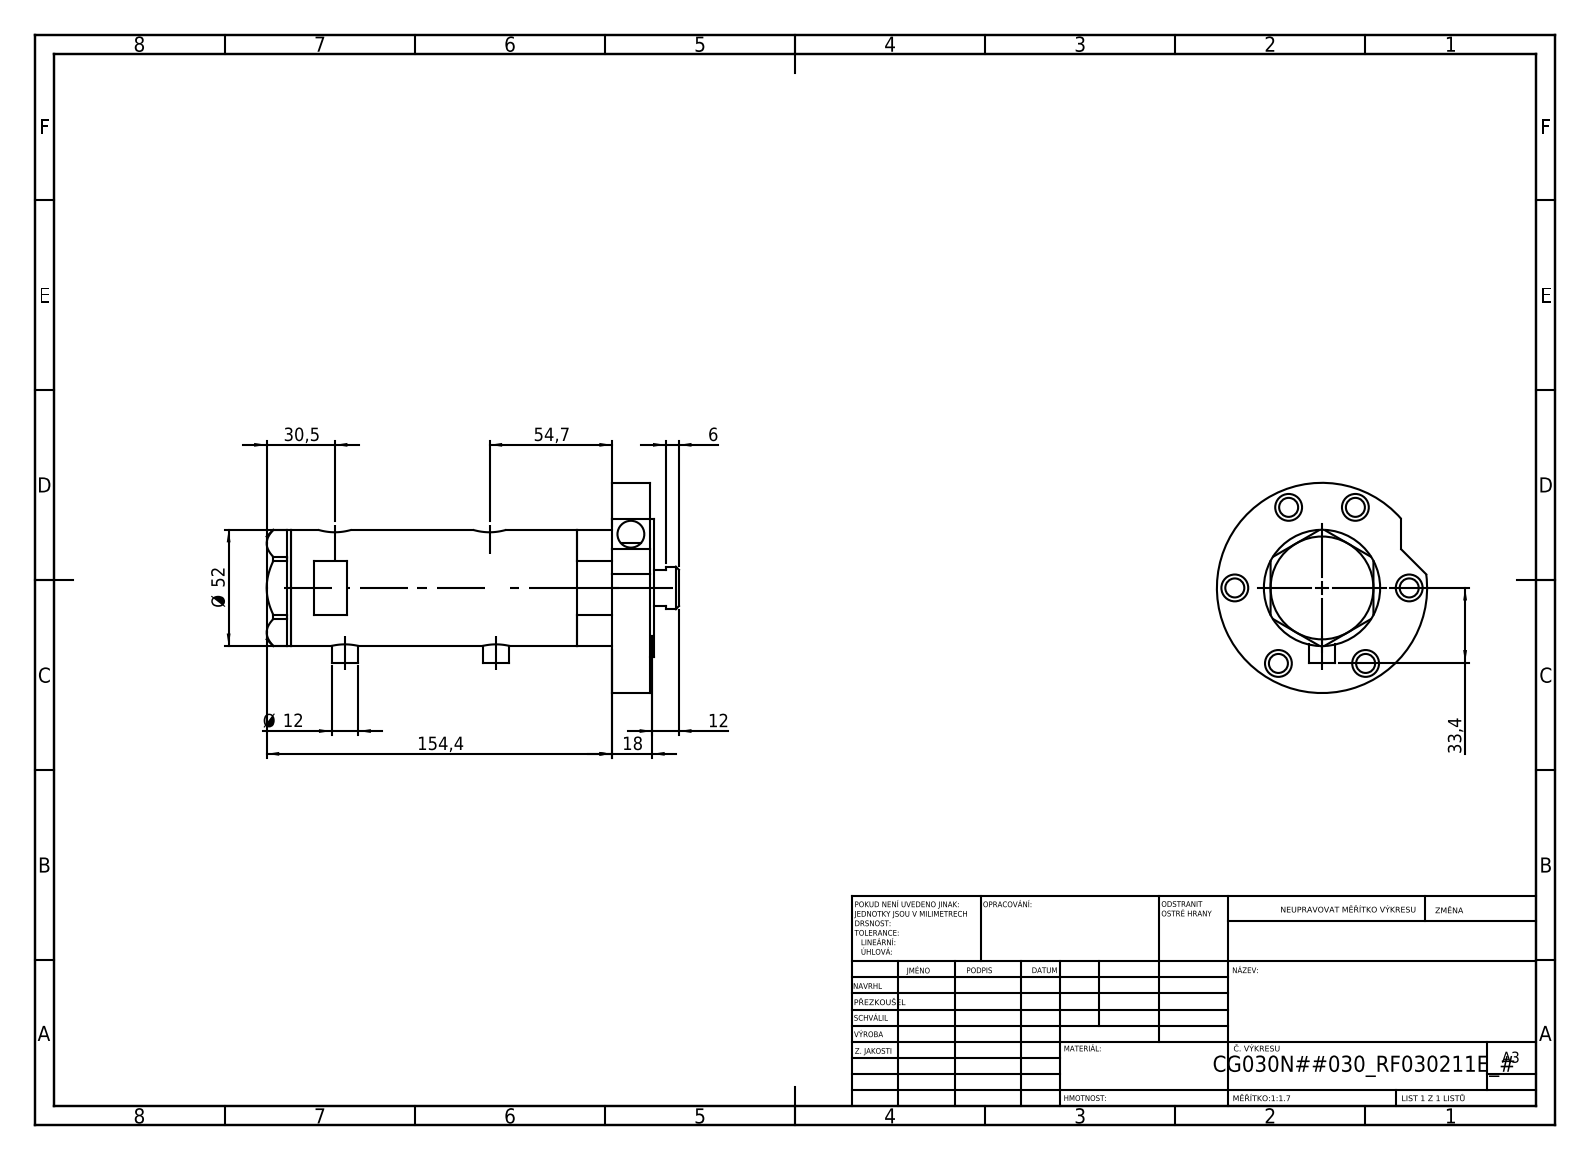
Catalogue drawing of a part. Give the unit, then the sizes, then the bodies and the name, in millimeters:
Units: millimetres
Overall size (bounding box): 184.4 × 94 × 94
Round holes (diameter × count): ⌀12 ×7, ⌀8.5 ×6, ⌀9.73 ×2, ⌀12.5 ×2, ⌀15 ×2, ⌀6.5 ×1, ⌀20 ×1, ⌀21.5 ×1, ⌀30 ×1, ⌀33 ×1, ⌀40 ×1, ⌀44 ×1
Round bosses / shafts (diameter × count): ⌀12 ×2, ⌀94 ×1, ⌀62 ×1, ⌀52 ×1, ⌀38 ×1, ⌀19 ×1
Main face-to-face distances: 17, 143.4, 160.4, 2, 162.4, 91.5, 51.9, 68.9, 11, 173.4
Hole centre spacings: 39, 43.34, 64.85, 67.55, 69.95, 77.83, 2.9, 4.5
Volume: 416 731 mm³ · Surface area: 100 916 mm²
Bodies: 5 solids, 178 faces (76 planar, 82 cylindrical, 20 other)
Part name (STEP PRODUCT): V270CG_MIDDLE; V270CG_FRONT; V270CG_RF211E; V270CG_VC (+1 more)
STEP written by: SolidWorks 2019 (CONFIG_CONTROL_DESIGN)
